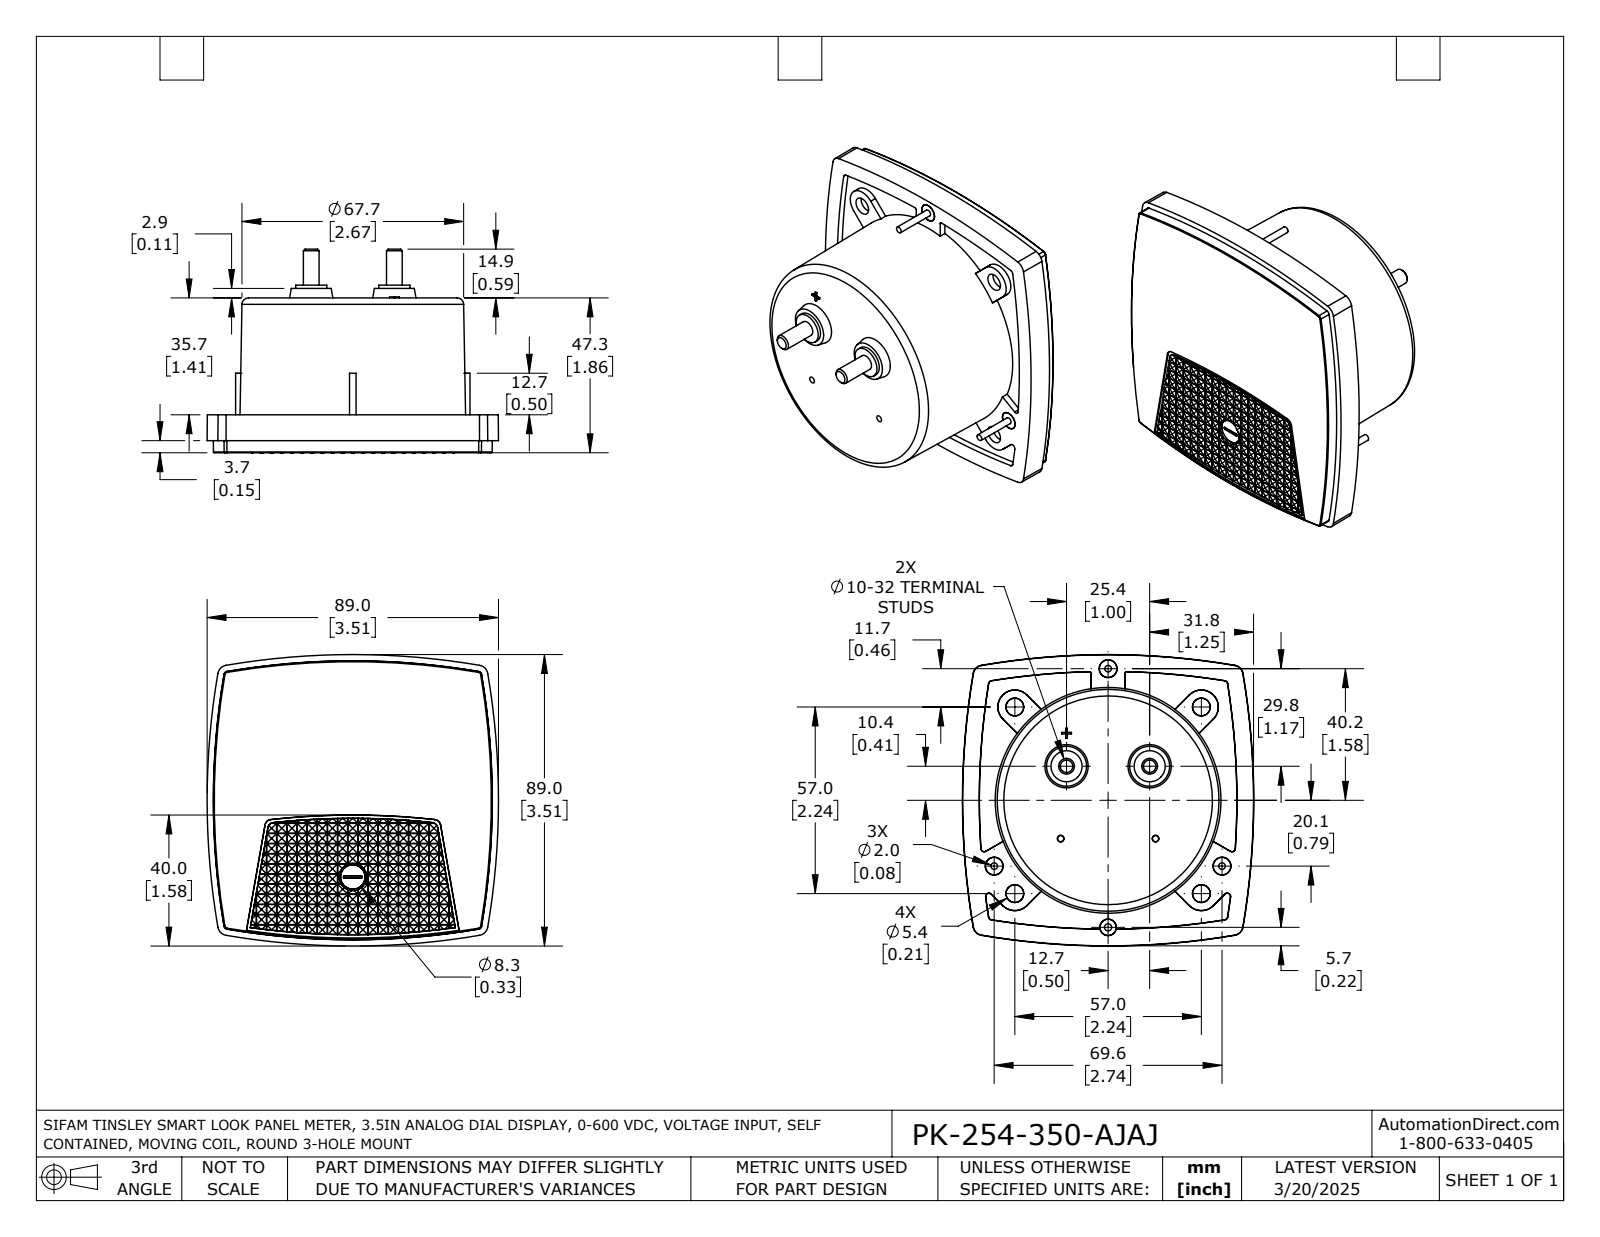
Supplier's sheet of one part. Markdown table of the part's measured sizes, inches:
| quantity | value |
| --- | --- |
| part name | PK-254-350-AJAJ |
| STEP written by | SolidWorks 2021 (AUTOMOTIVE_DESIGN) |
| units | inches |
| bodies | 1 solid, 1078 faces (950 planar, 23 cylindrical, 105 other) |
| overall size | 3.505 × 3.505 × 2.453 |
| volume | 12.99 in³ |
| surface area | 44.29 in² |
| round holes (diameter × count) | 0.087 × 1 |
| round bosses / shafts (diameter × count) | 0.213 × 3, 0.079 × 3, 0.374 × 2, 0.189 × 2 |
| partial cylindrical surfaces (radius × count) | 8.961 × 1 |
| main face-to-face distances | 1.862, 1.406, 0.457, 0.079, 1.484, 0.378, 0.024, 0.096, 0.072, 0.12 |
